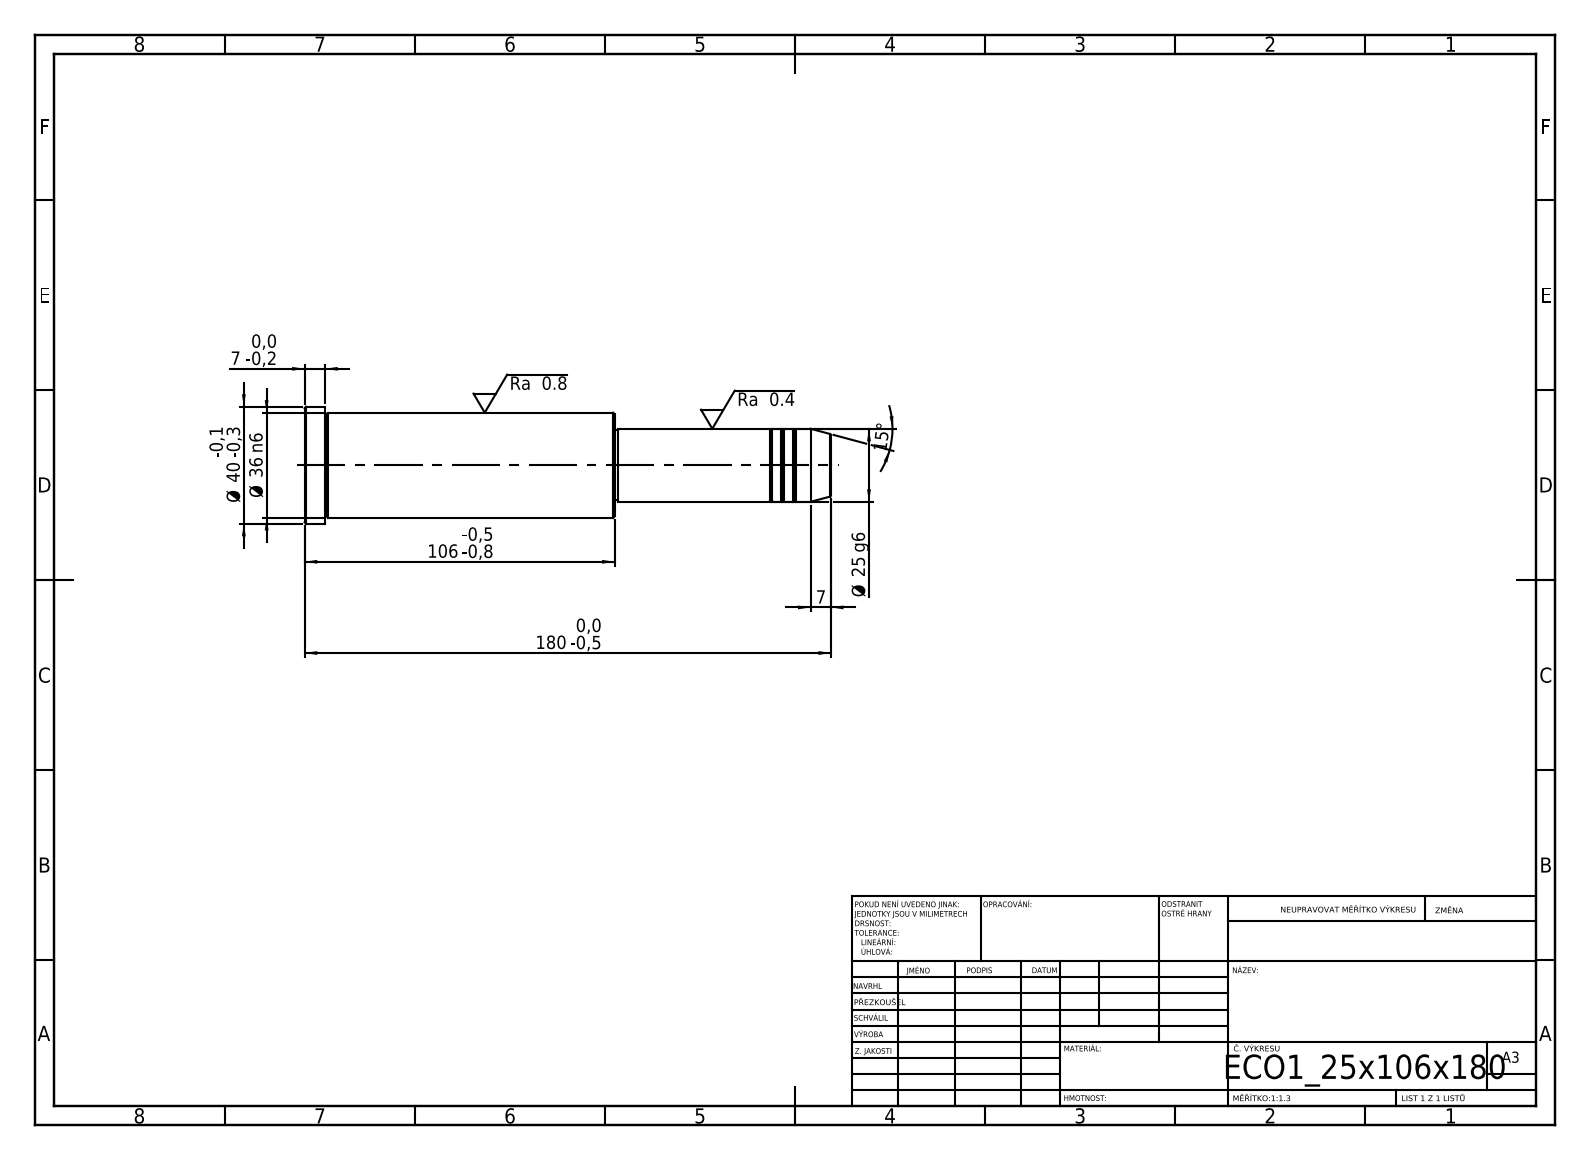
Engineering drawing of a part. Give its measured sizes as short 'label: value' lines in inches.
written by: SolidWorks 2019 (CONFIG_CONTROL_DESIGN)
unit: in
bodies: 1 solid, 43 faces (5 planar, 14 cylindrical, 24 other)
size: 7.087 × 1.575 × 1.575
volume: 8.86 in³; area: 31.66 in²
bosses: 1× ⌀1.575, 1× ⌀1.417, 1× ⌀0.984, 1× ⌀0.945
face distances: 4.173, 2.913, 7.087, 6.811, 3.898, 0.276, 2.874, 0.039, 3.937, 4.213
